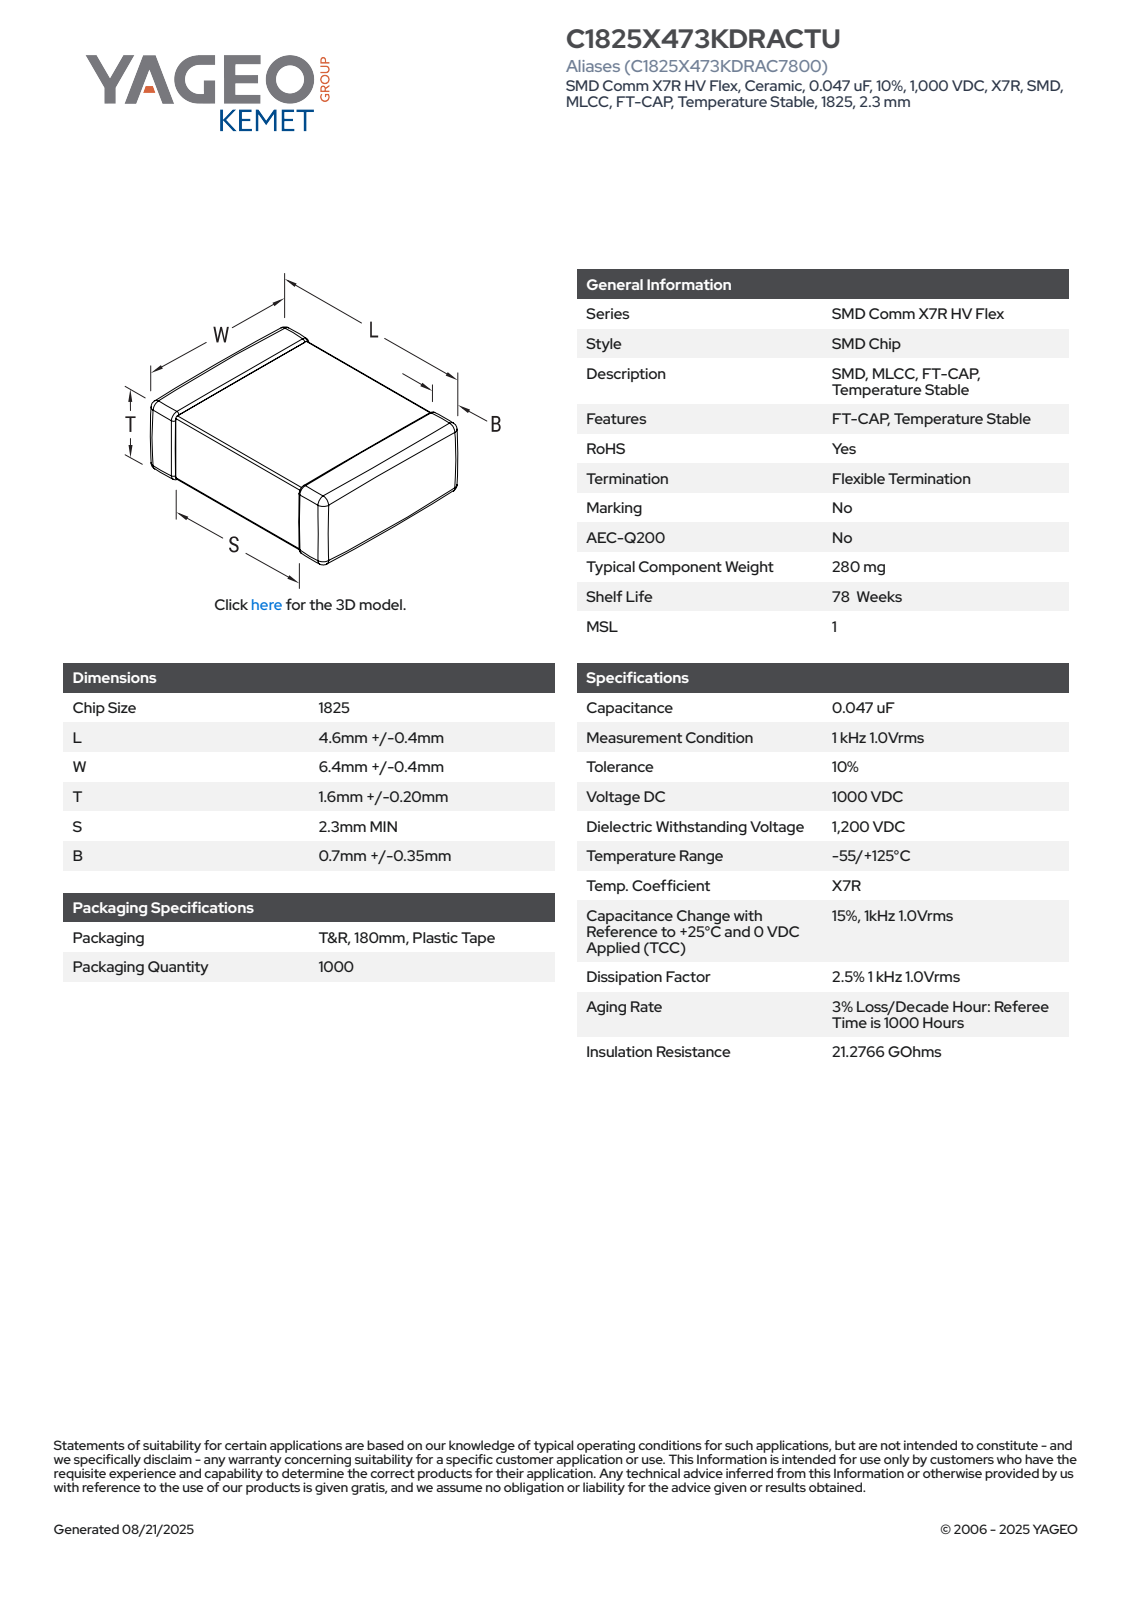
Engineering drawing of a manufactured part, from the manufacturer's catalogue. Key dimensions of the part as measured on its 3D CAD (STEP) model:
Part name (STEP PRODUCT): CCS_CCSTD_1825_L5W6.8T1.8B0.7
STEP written by: SolidWorks 2021 (AUTOMOTIVE_DESIGN)
Units: millimetres
Bodies: 4 solids, 125 faces (71 planar, 38 cylindrical, 16 other)
Overall size (bounding box): 6.8 × 5 × 1.8
Volume: 54 mm³ · Surface area: 113 mm²
Partial cylindrical surfaces — rounded edges, fillets, slot ends (radius × count): R0.14 ×24
Main face-to-face distances: 1.66, 1.52, 1.8, 5, 6.66, 6.52, 6.8, 1, 2.3, 1.7
